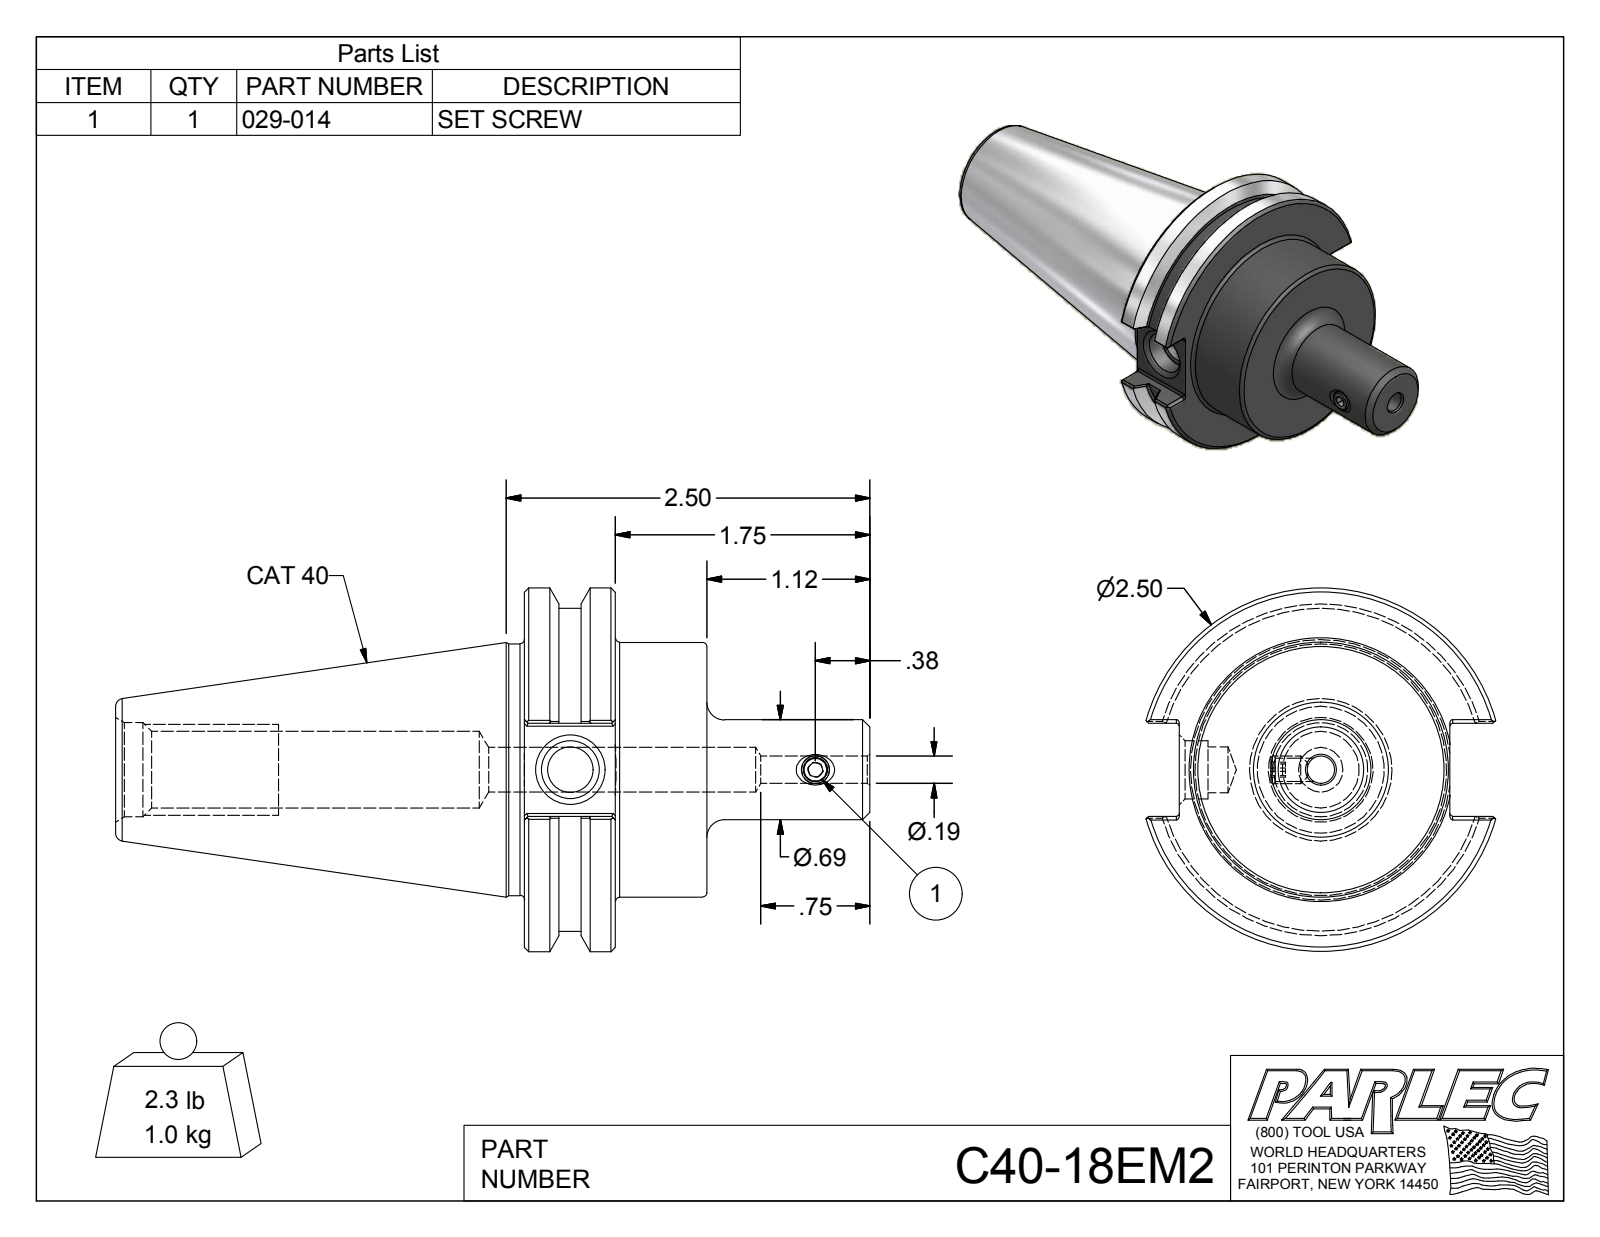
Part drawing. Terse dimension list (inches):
name: C40-18EM2; C40-18EM2-1; 029-014
written by: Autodesk Inventor 2012 (AUTOMOTIVE_DESIGN)
unit: in
bodies: 2 solids, 61 faces (20 planar, 16 cylindrical, 25 other)
size: 5.188 × 2.5 × 2.417
volume: 8.133 in³; area: 37.81 in²
holes: 1× ⌀0.156, 1× ⌀0.187, 1× ⌀0.28, 1× ⌀0.527, 1× ⌀0.563, 1× ⌀0.648
bosses: 1× ⌀2.5, 1× ⌀2.219, 1× ⌀1.75, 1× ⌀0.687, 1× ⌀0.19
face distances: 0.625, 1.255, 0.63, 0.64, 2.375, 1.75, 1.12, 2.813, 3.437, 4.067
hole spacings: 1.685
